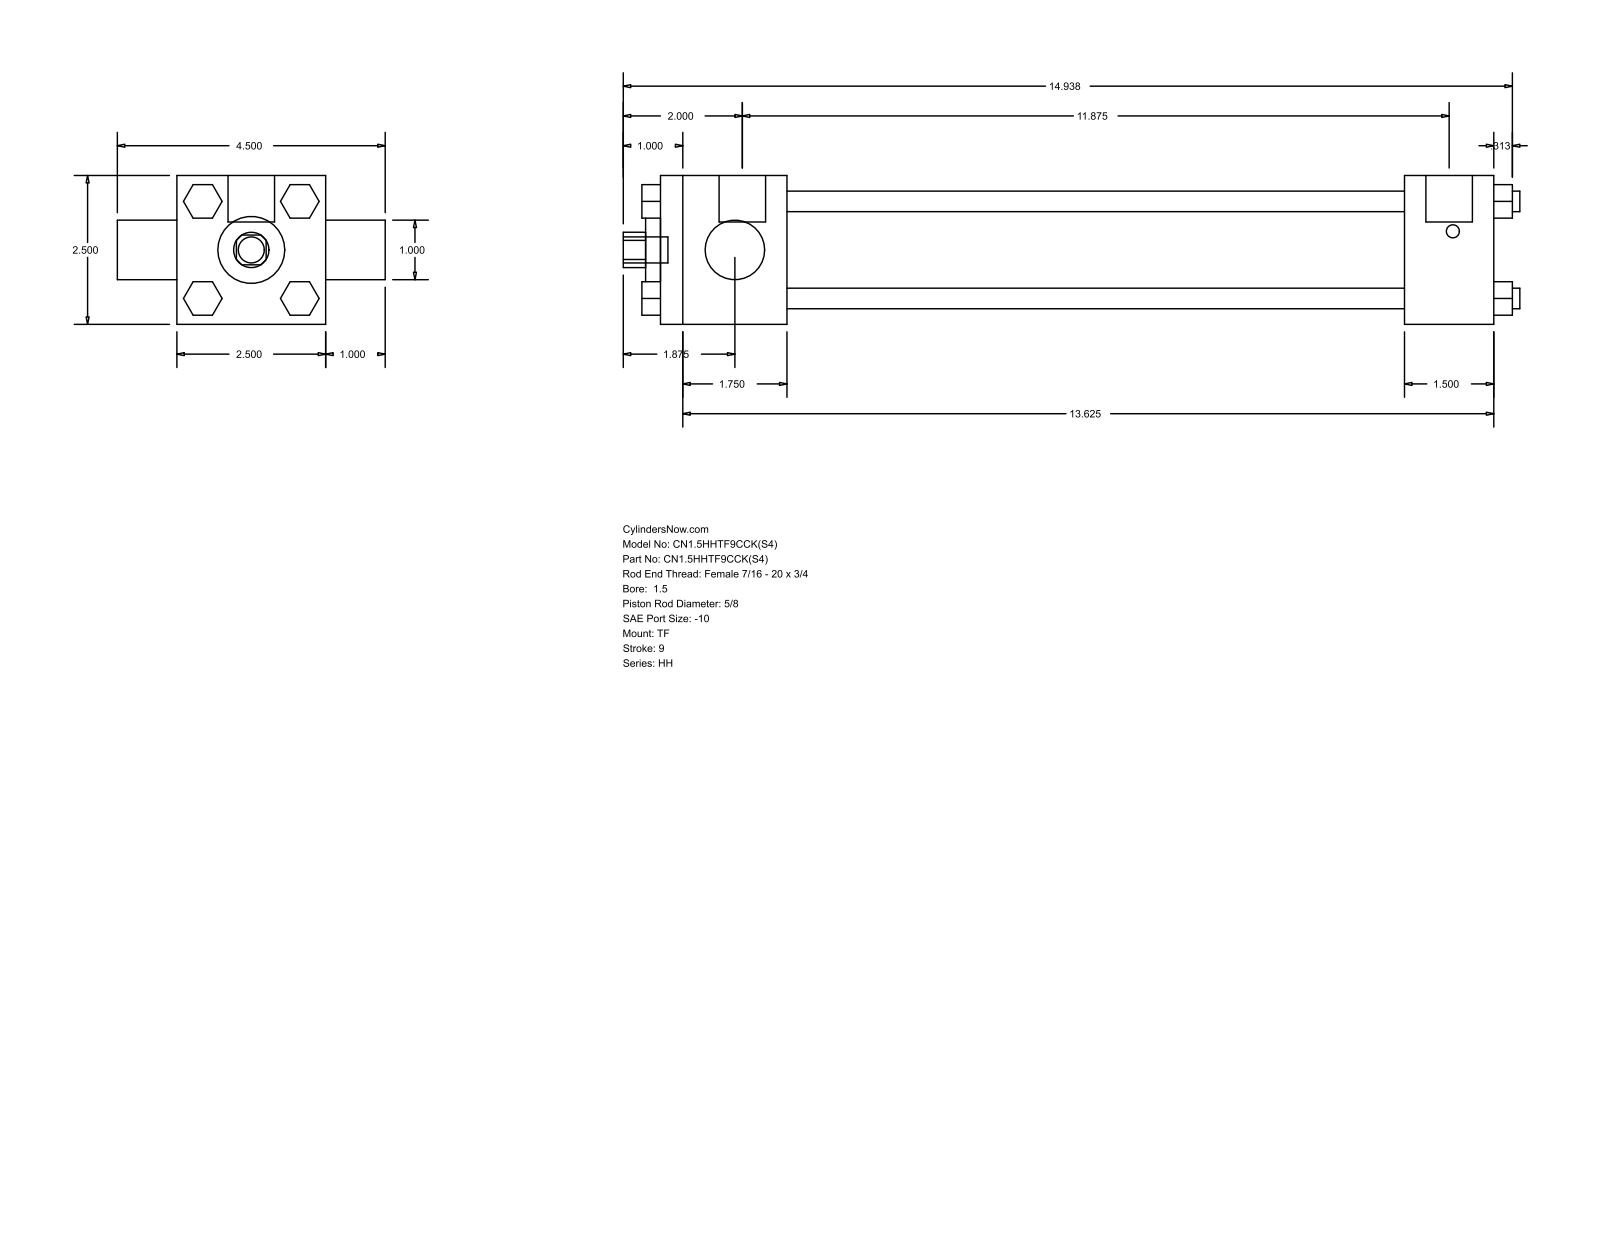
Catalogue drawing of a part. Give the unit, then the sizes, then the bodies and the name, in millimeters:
Units: millimetres
Overall size (bounding box): 382.59 × 114.3 × 63.5
Round holes (diameter × count): ⌀15.88 ×1, ⌀25.4 ×1, ⌀28.57 ×1, ⌀44.45 ×1
Round bosses / shafts (diameter × count): ⌀8.76 ×4, ⌀5.56 ×3, ⌀19.84 ×2, ⌀11.11 ×1
Partial cylindrical surfaces — rounded edges, fillets, slot ends (radius × count): R7.54 ×1
Main face-to-face distances: 63.5, 355.6, 38.1, 53.97, 301.63, 317.5, 263.53, 25.4, 20.7, 14.29
Bodies: 0 solids, 120 faces (92 planar, 28 cylindrical, 0 other)
Part name (STEP PRODUCT): HH_TF__0150_0.625
STEP written by: GSSL Pune (CONFIG_CONTROL_DESIGN)
